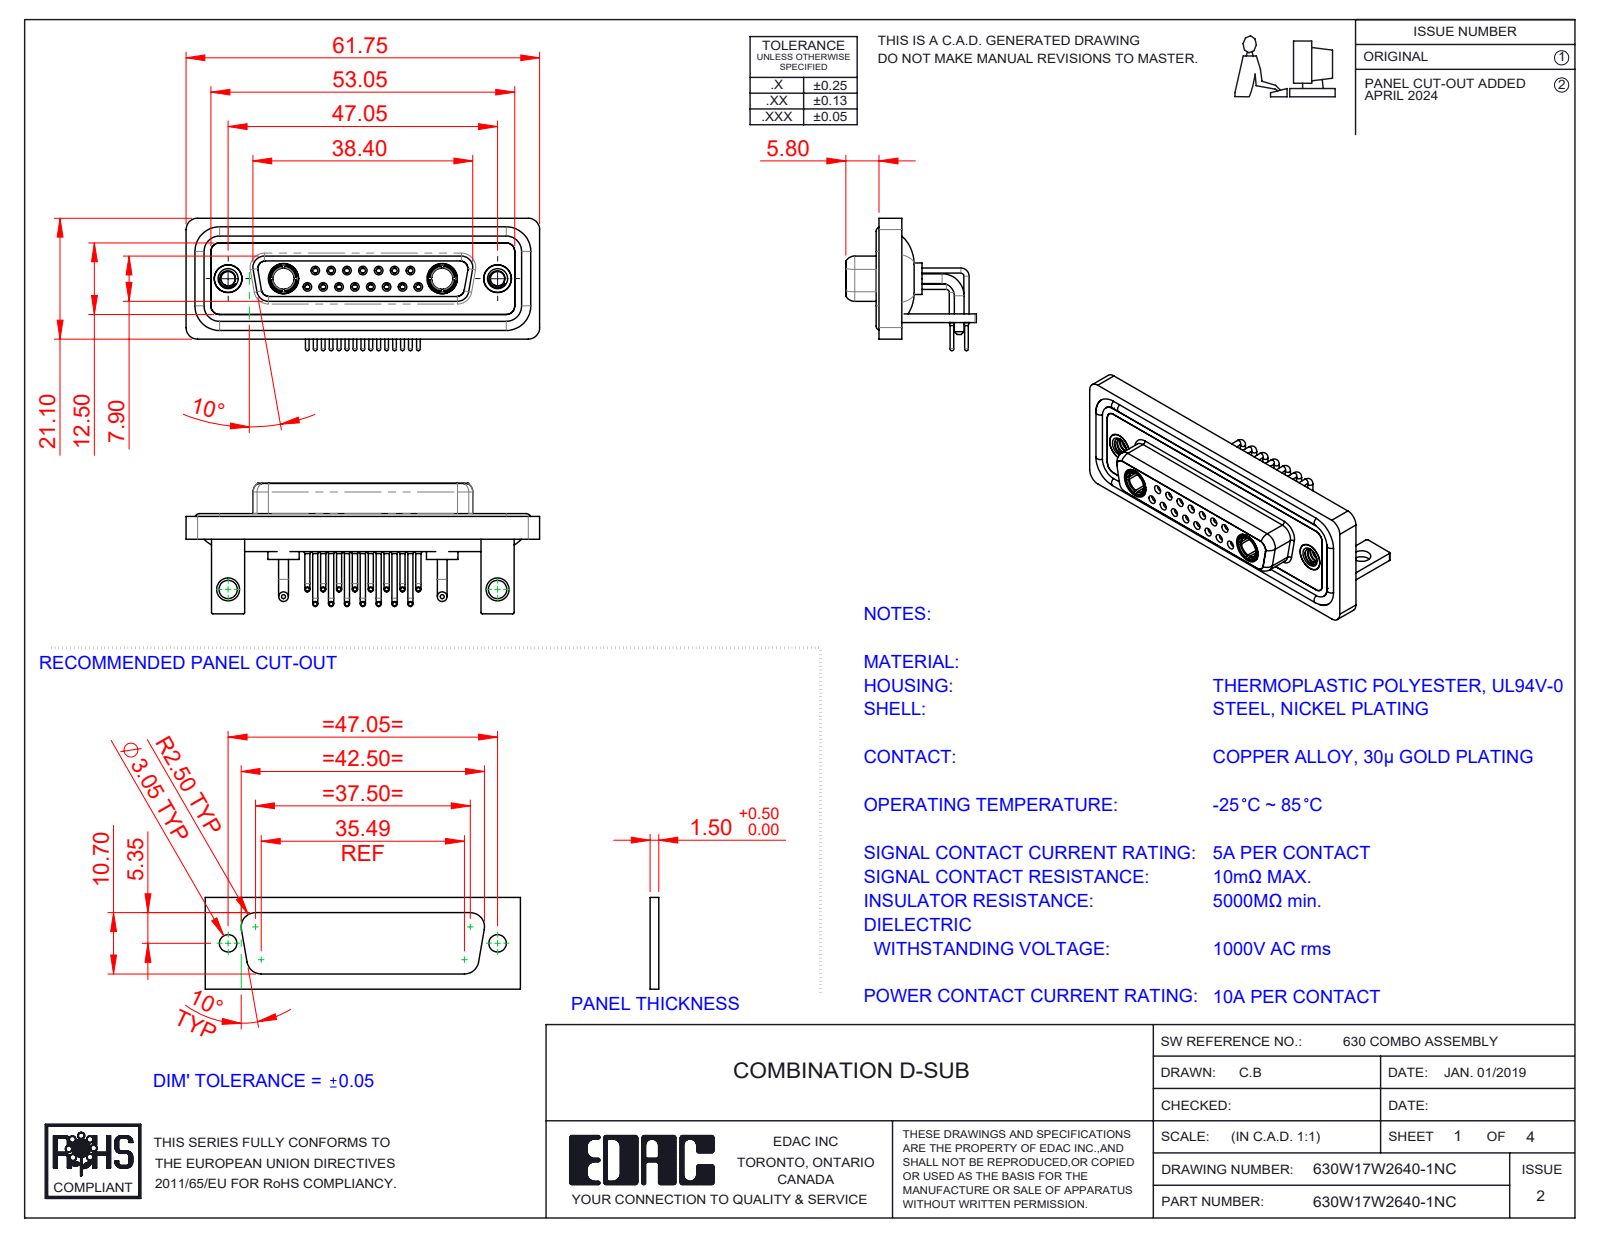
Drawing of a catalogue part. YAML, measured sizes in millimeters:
part_name: "630Combo Contact Row 2_50 Contacts; 630Combo Shell Front_25 Contacts; 630Combo Stabilizer Bracket_50 Contacts; Power Socket_10A RA (+6 more)"
step_written_by: "SolidWorks 2023 (CONFIG_CONTROL_DESIGN)"
units: millimeters
bodies: {solids: 28, faces: 1379, planar: 408, cylindrical: 605, other: 366}
overall_size: [61.75, 23.12, 22.8]
volume: 8730
surface_area: 15167
round_holes:
  - {diameter: 0.9, count: 15}
  - {diameter: 1.1, count: 15}
  - {diameter: 1.5, count: 15}
  - {diameter: 2, count: 15}
  - {diameter: 1.6, count: 8}
  - {diameter: 1.7, count: 7}
  - {diameter: 4.85, count: 4}
  - {diameter: 2.5, count: 2}
  - {diameter: 3.2, count: 2}
  - {diameter: 3.7, count: 2}
  - {diameter: 4, count: 2}
  - {diameter: 4.05, count: 2}
round_bosses_or_shafts:
  - {diameter: 0.9, count: 15}
  - {diameter: 0.65, count: 15}
  - {diameter: 1.6, count: 11}
  - {diameter: 1.7, count: 4}
  - {diameter: 5.5, count: 2}
  - {diameter: 5.2, count: 2}
  - {diameter: 4.96, count: 2}
  - {diameter: 4.95, count: 2}
partial_cylinders:
  - {radius: 2, count: 19}
  - {radius: 1.5, count: 18}
  - {radius: 0.25, count: 16}
  - {radius: 1.35, count: 8}
  - {radius: 1.6, count: 8}
  - {radius: 0.5, count: 5}
  - {radius: 0.6, count: 4}
  - {radius: 0.65, count: 4}
face_to_face_distances: [0.4, 1.8, 2.9, 3.7, 1.5, 4.1, 1.1, 1.4, 1.6, 3.1]
hole_center_spacings: [3.16, 2.77, 5.54, 8.31, 5.04, 7.49, 11.08, 5.03]
